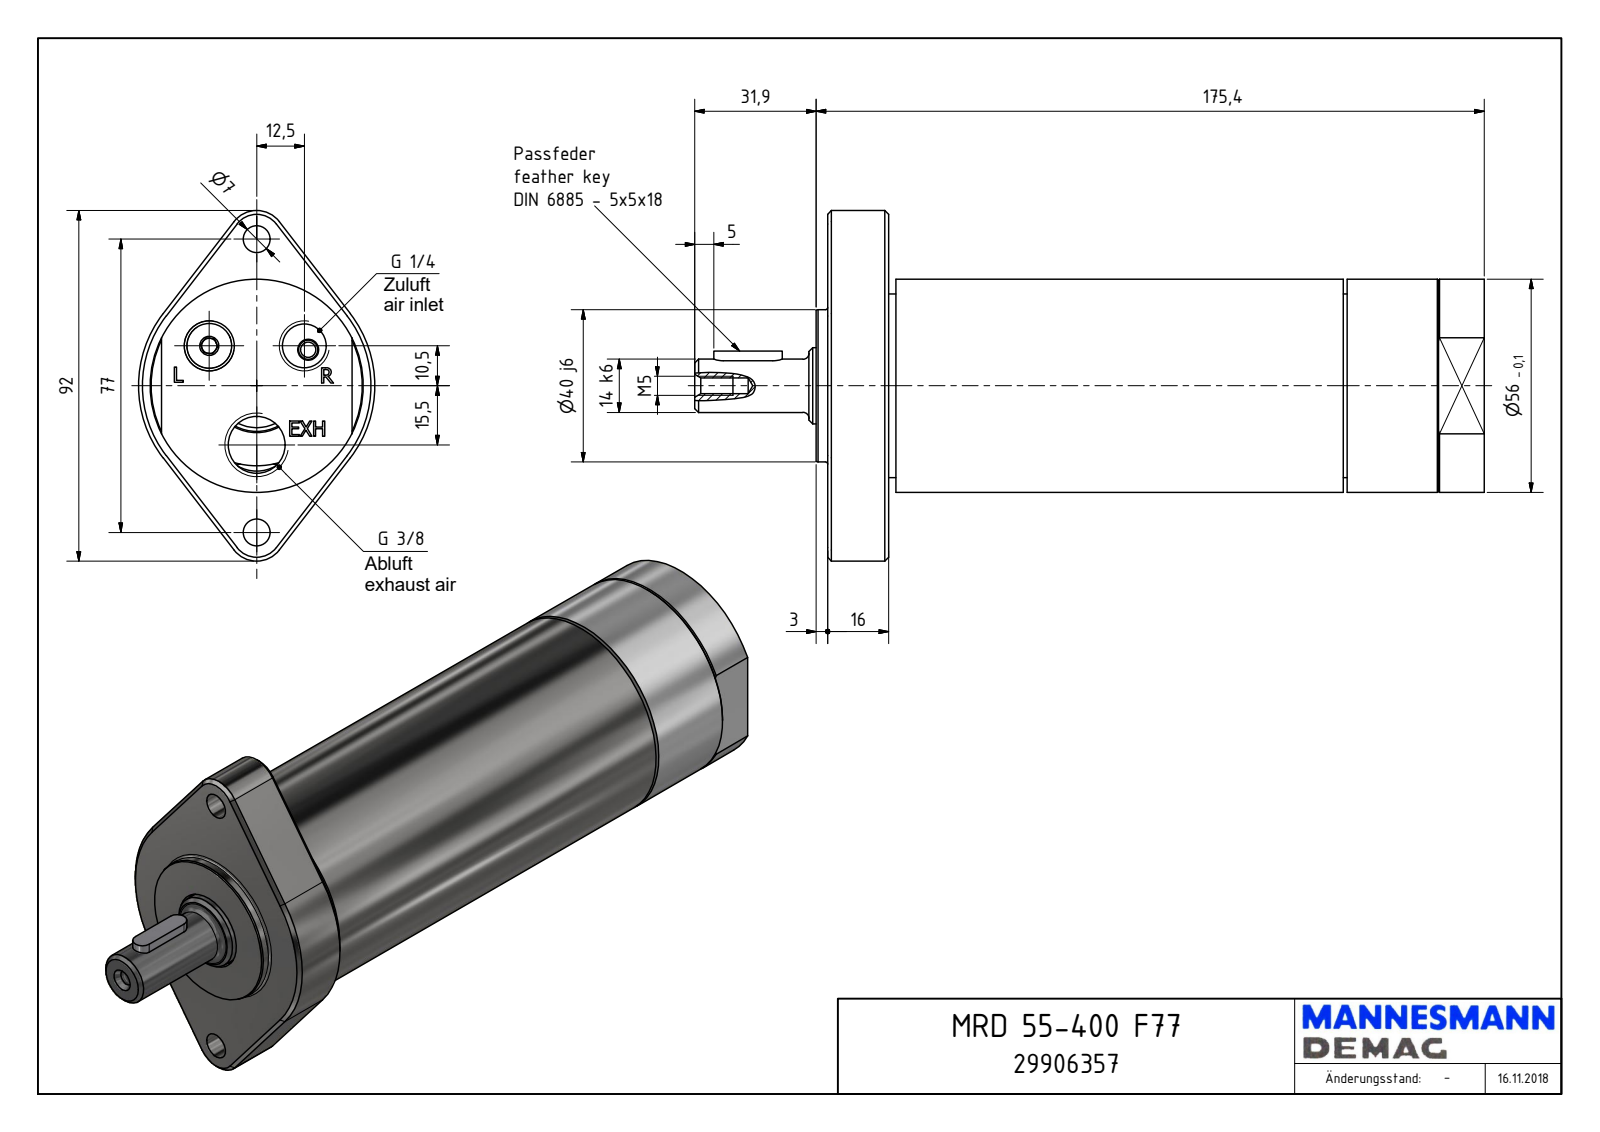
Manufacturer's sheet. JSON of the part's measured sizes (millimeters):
{"part_name": "MRD 55-400 F77_29906357", "step_written_by": "Autodesk Inventor 2018 (AUTOMOTIVE_DESIGN)", "units": "millimeters", "bodies": {"solids": 1, "faces": 198, "planar": 116, "cylindrical": 32, "other": 50}, "overall_size": [207.3, 92, 62], "volume_mm3": 446084, "surface_area_mm2": 46635, "round_holes": [[7, 2], [4, 1], [4.13, 1], [11.45, 1], [14.95, 1], [21, 1], [21.25, 1], [23.54, 1], [26, 1], [48.38, 1]], "round_bosses_or_shafts": [[56, 1], [48.18, 1], [40, 1], [19.95, 1], [14, 1]], "partial_cylinders_radius": [[2.5, 2], [6, 2], [7.5, 2], [22.24, 1], [23, 1], [31, 1]], "face_to_face_distances": [172.4, 16, 156.4, 3, 19, 175.4, 1.9, 20.9, 17.9, 154.5], "hole_center_spacings": [16.32, 28.85, 30.66, 38.5, 50.57, 15.5, 23, 25]}
